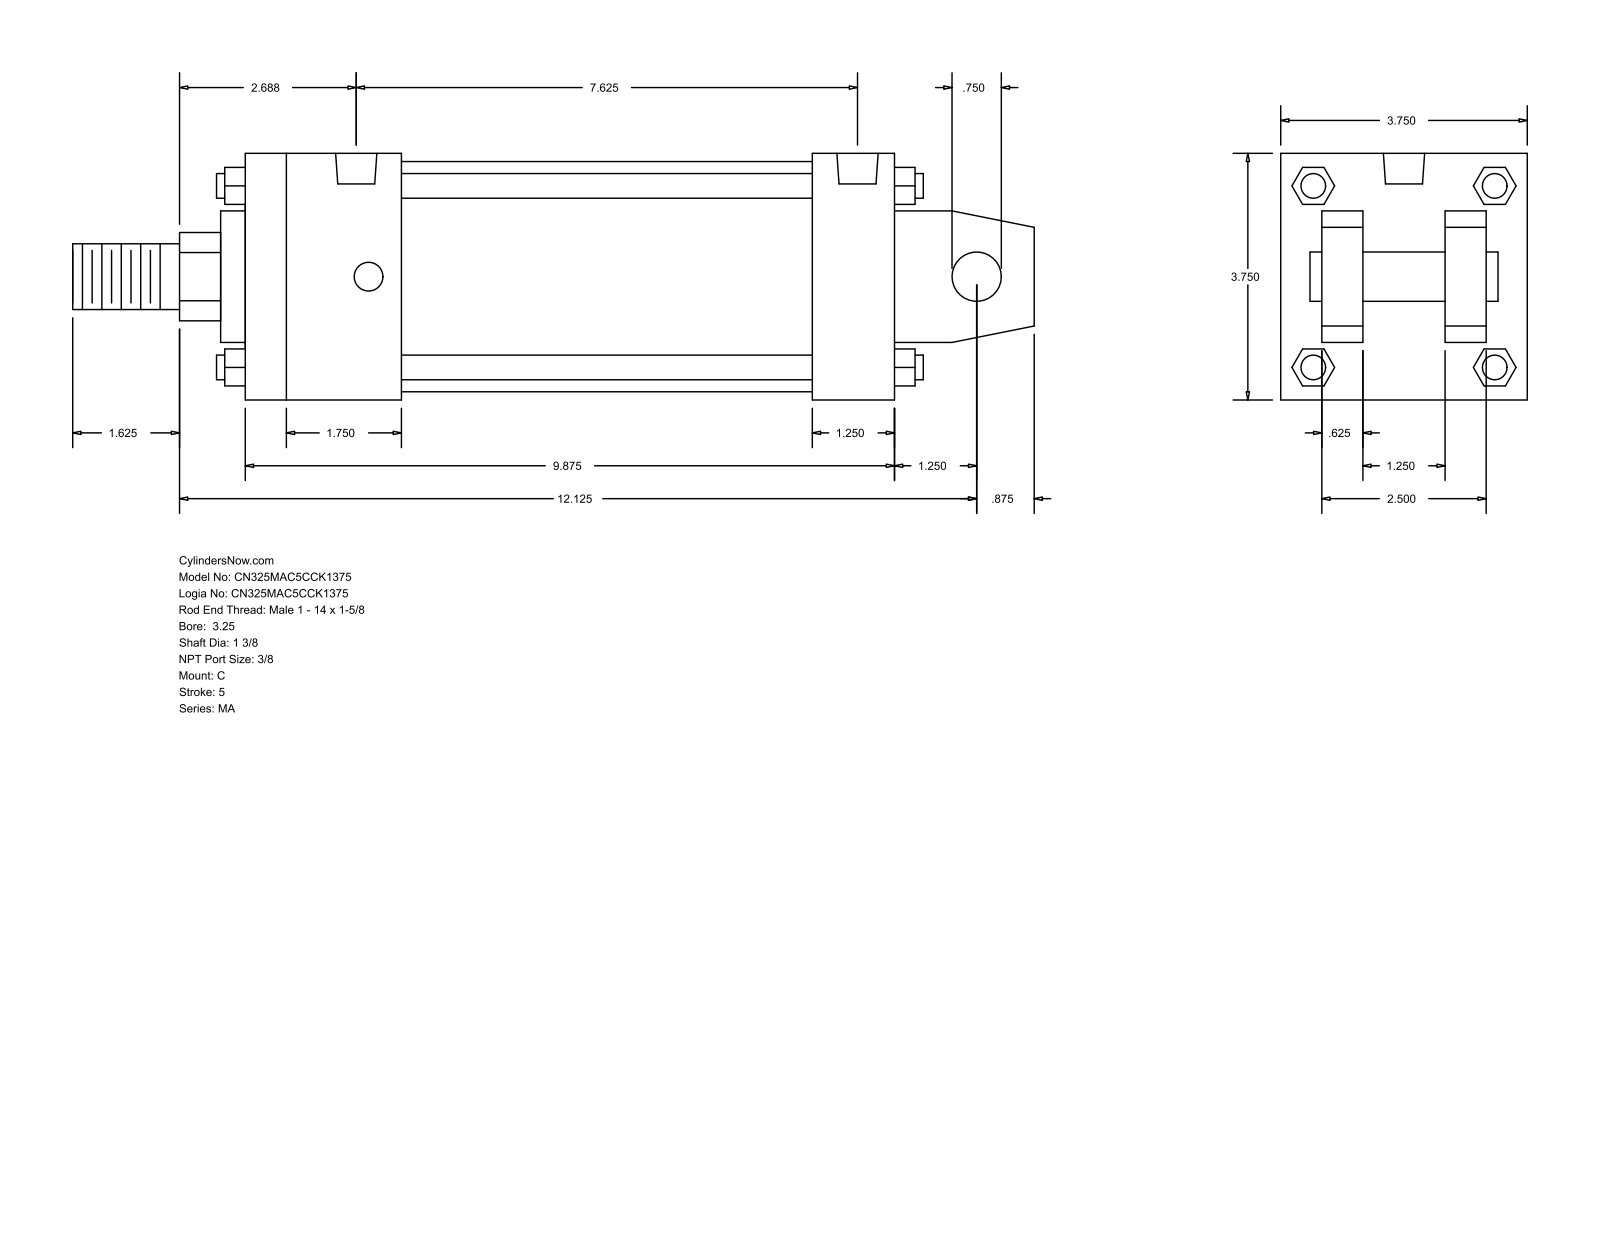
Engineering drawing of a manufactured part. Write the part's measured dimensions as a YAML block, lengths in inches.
part_name: "MA_C__0325_1.375"
step_written_by: "GSSL Pune (CONFIG_CONTROL_DESIGN)"
units: inches
bodies: {solids: 0, faces: 139, planar: 108, cylindrical: 31, other: 0}
overall_size: [14.625, 3.75, 3.75]
round_holes:
  - {diameter: 0.437, count: 4}
  - {diameter: 0.627, count: 2}
round_bosses_or_shafts:
  - {diameter: 0.375, count: 4}
  - {diameter: 3.5, count: 1}
  - {diameter: 2, count: 1}
  - {diameter: 1.375, count: 1}
  - {diameter: 1, count: 1}
  - {diameter: 0.75, count: 1}
partial_cylinders:
  - {radius: 0.672, count: 1}
face_to_face_distances: [3.75, 0.625, 2.5, 9.875, 1.25, 1.25, 3.125, 1.875, 8.625, 2.375]
hole_center_spacings: [7.25, 0.187, 0.188, 7.437, 7.438, 7.625]
